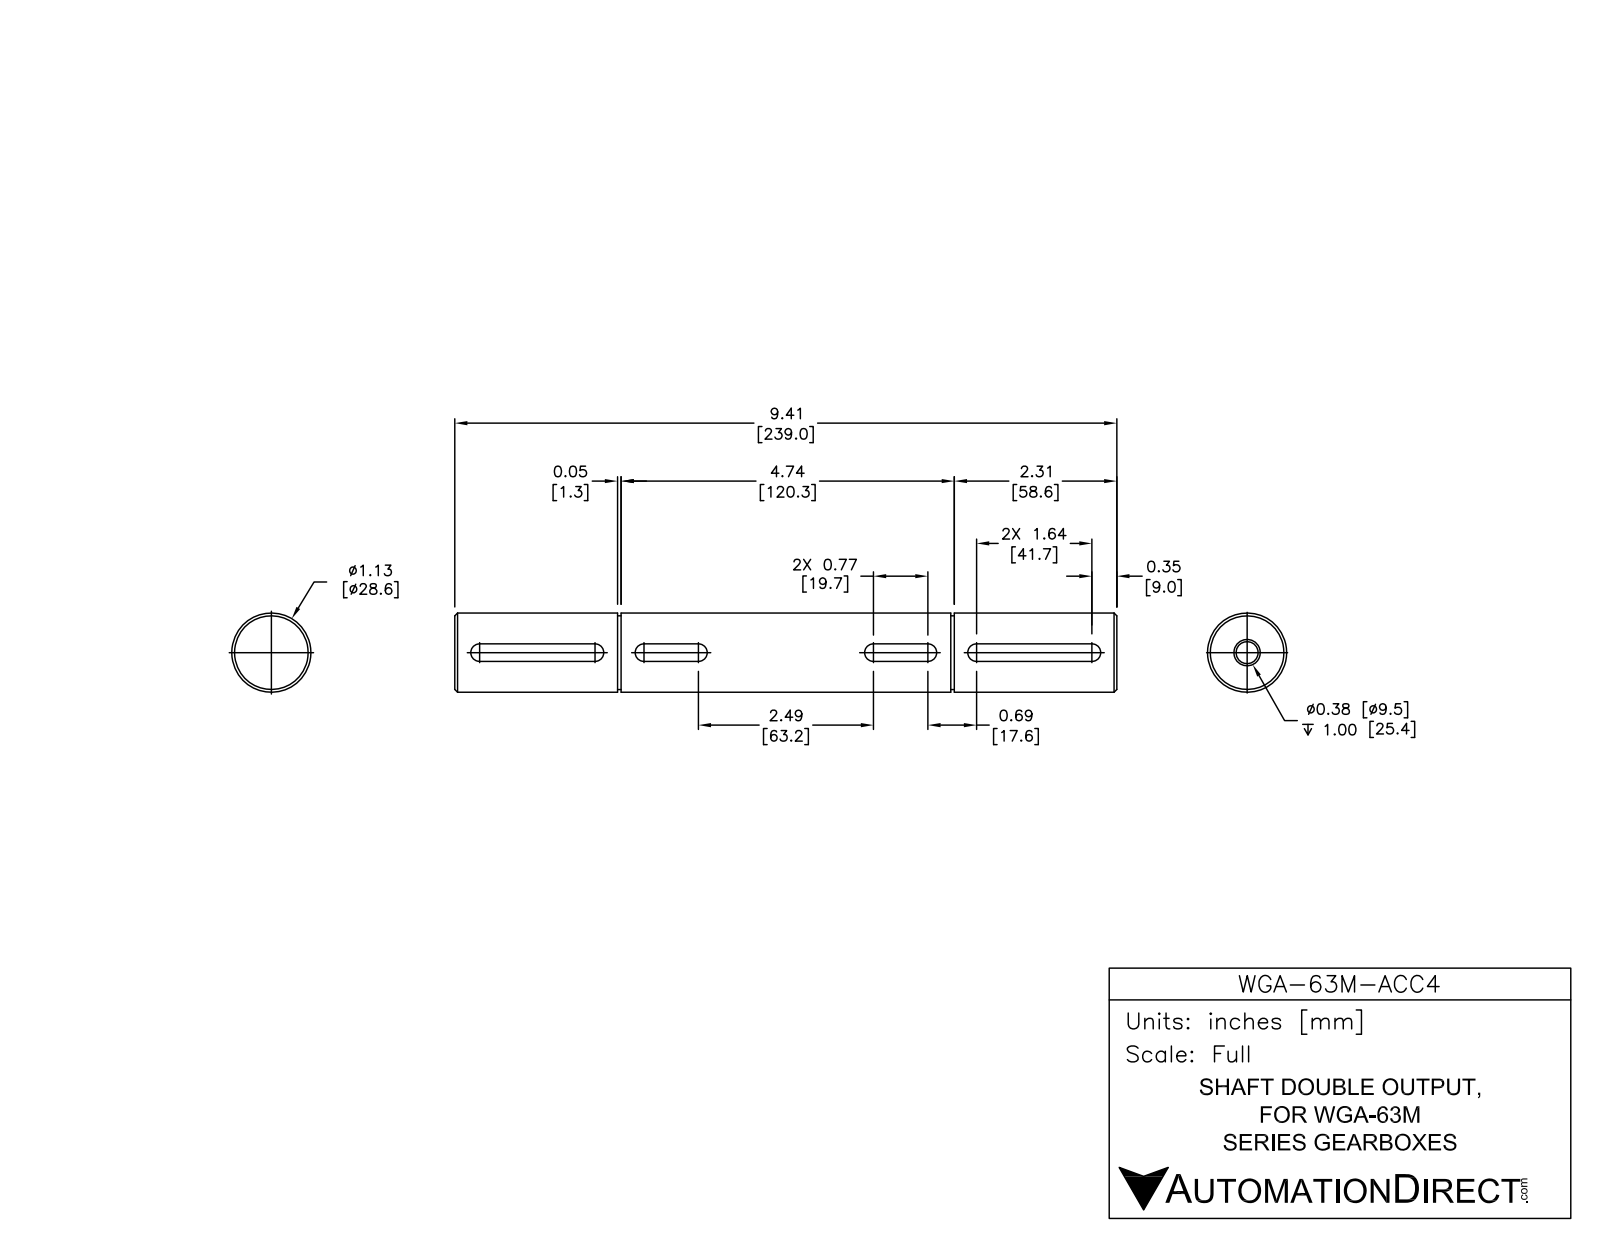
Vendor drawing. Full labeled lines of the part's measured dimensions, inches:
Part name (STEP PRODUCT): WGA-63M-ACC4
STEP written by: SolidWorks 2014 (AUTOMOTIVE_DESIGN)
Units: inches
Bodies: 1 solid, 47 faces (19 planar, 22 cylindrical, 6 other)
Overall size (bounding box): 9.409 × 1.125 × 1.125
Volume: 9.044 in³ · Surface area: 38.34 in²
Round holes (diameter × count): ⌀0.313 ×1, ⌀0.375 ×1
Round bosses / shafts (diameter × count): ⌀1.125 ×1, ⌀1.047 ×1
Partial cylindrical surfaces — rounded edges, fillets, slot ends (radius × count): R0.125 ×8
Main face-to-face distances: 9.409, 0.25, 0.25, 0.051, 4.736, 0.25, 2.313, 2.365, 7.05, 7.101
